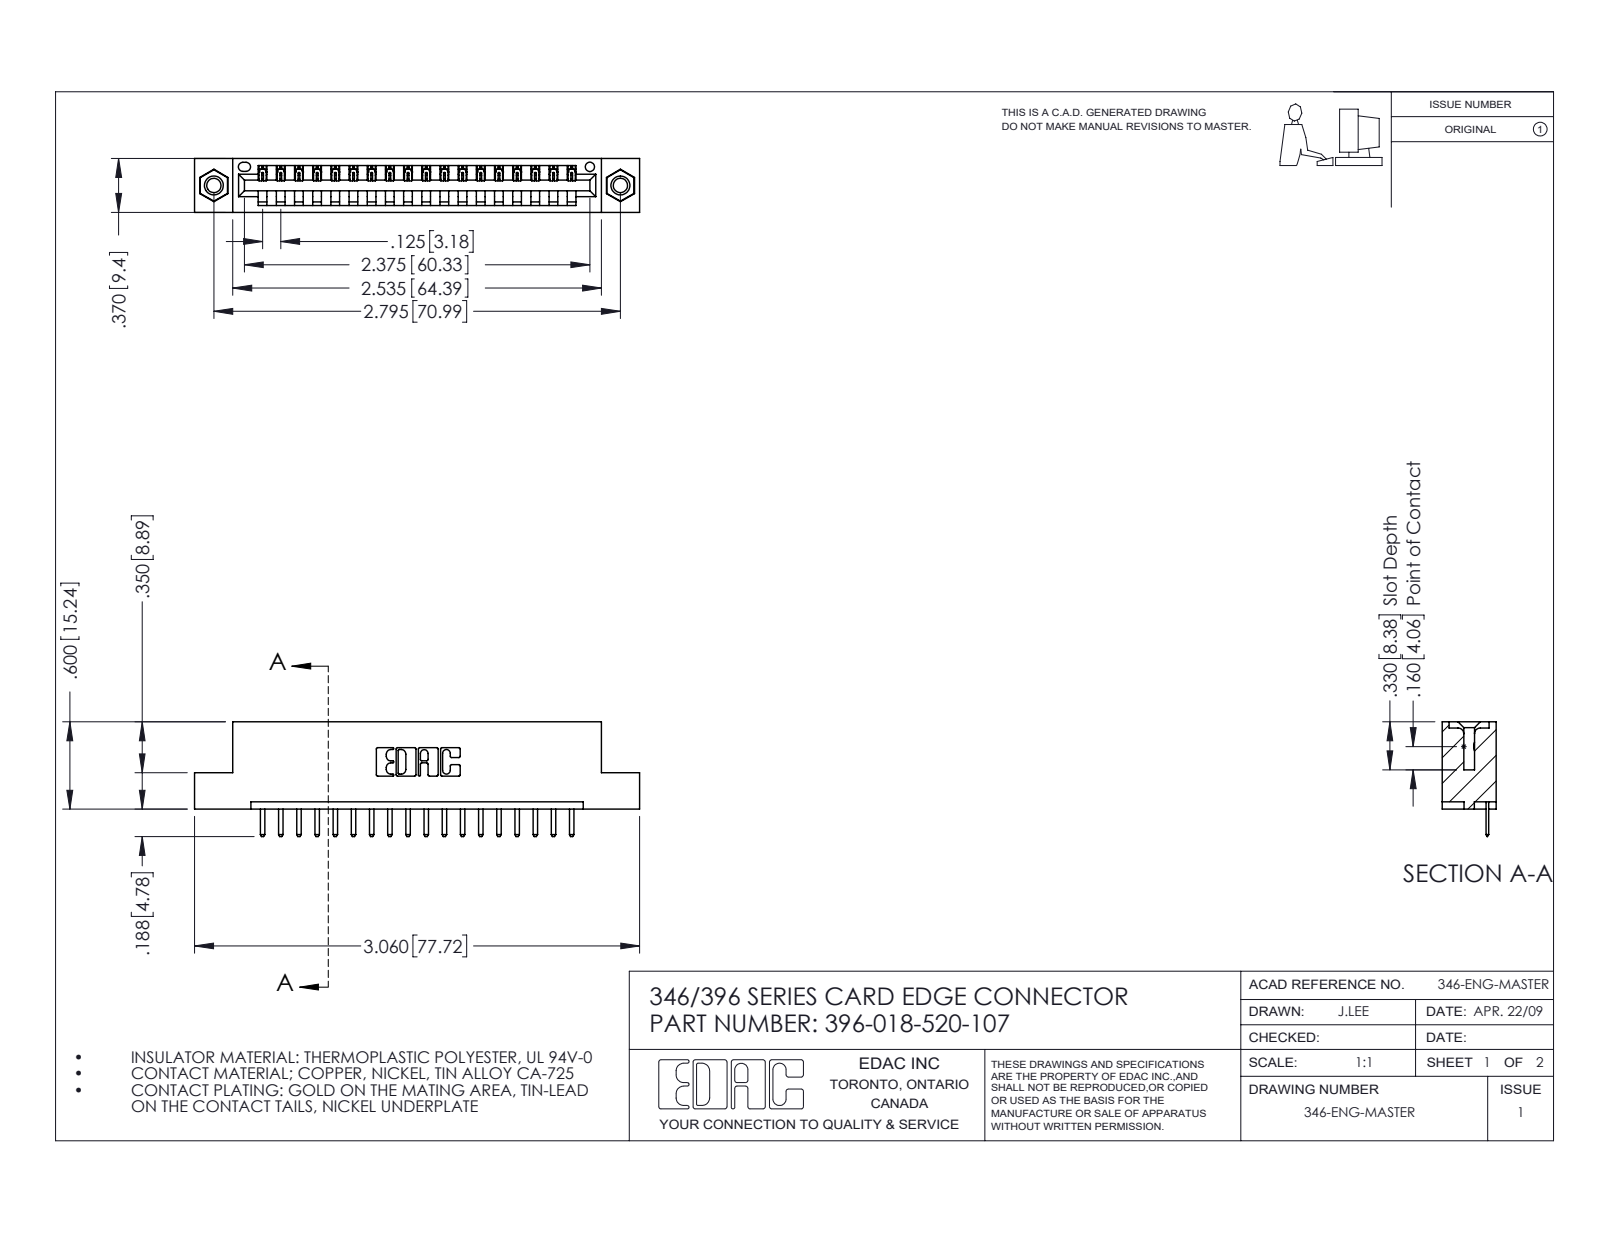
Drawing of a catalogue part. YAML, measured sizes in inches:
part_name: "345-292-001_345-293-120; 396-018-520-107; 346 Part_Flush Mounting Lugs - 0.156 Dia-TI; 345-250-001_345-250-005-103"
step_written_by: "SolidWorks 2016 (CONFIG_CONTROL_DESIGN)"
units: inches
bodies: {solids: 21, faces: 1298, planar: 864, cylindrical: 418, other: 16}
overall_size: [3.06, 0.788, 0.37]
volume: 0.44
surface_area: 13.35
round_holes:
  - {diameter: 0.098, count: 2}
  - {diameter: 0.125, count: 2}
  - {diameter: 0.156, count: 2}
  - {diameter: 0.064, count: 1}
round_bosses_or_shafts:
  - {diameter: 0.155, count: 2}
partial_cylinders:
  - {radius: 0.01, count: 38}
  - {radius: 0.006, count: 36}
  - {radius: 0.01, count: 22}
  - {radius: 0.007, count: 6}
  - {radius: 0.031, count: 6}
  - {radius: 0.026, count: 3}
  - {radius: 0.031, count: 2}
  - {radius: 0.04, count: 2}
face_to_face_distances: [0.048, 0.322, 0.37, 0.25, 0.148, 0.222, 0.1, 0.174, 0.072, 0.298]
hole_center_spacings: [0.246, 2.588, 2.795]
